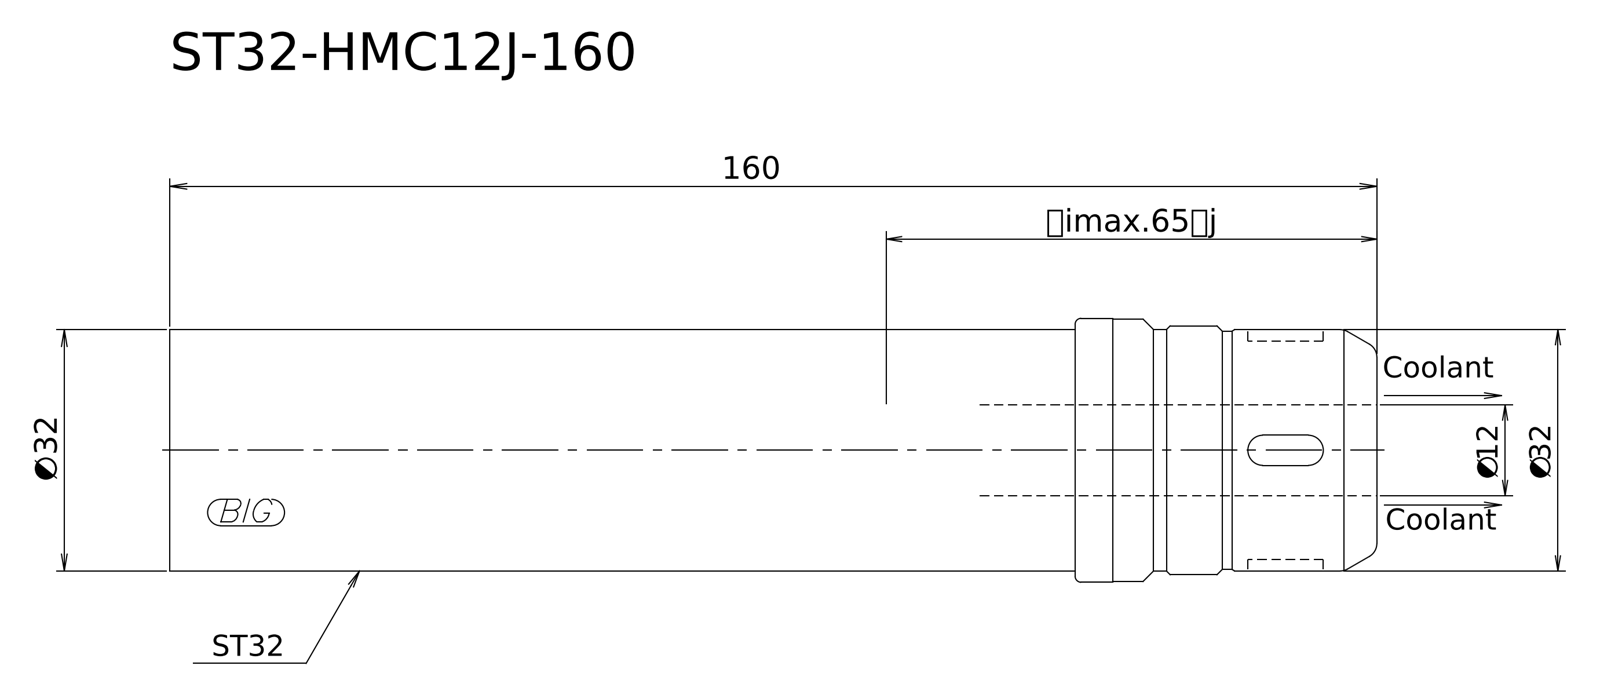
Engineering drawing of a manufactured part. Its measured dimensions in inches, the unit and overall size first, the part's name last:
Units: inches
Overall size (bounding box): 6.299 × 1.378 × 1.378
Round bosses / shafts (diameter × count): ⌀1.378 ×1, ⌀1.299 ×1, ⌀1.26 ×1, ⌀1.244 ×1
Main face-to-face distances: 6.299, 1.575, 4.724
Volume: 7.933 in³ · Surface area: 27.71 in²
Bodies: 1 solid, 14 faces (3 planar, 6 cylindrical, 5 other)
STEP written by: Kubotek KeyCreator 2011 V10.0.2 (22737) (automotive_design)
